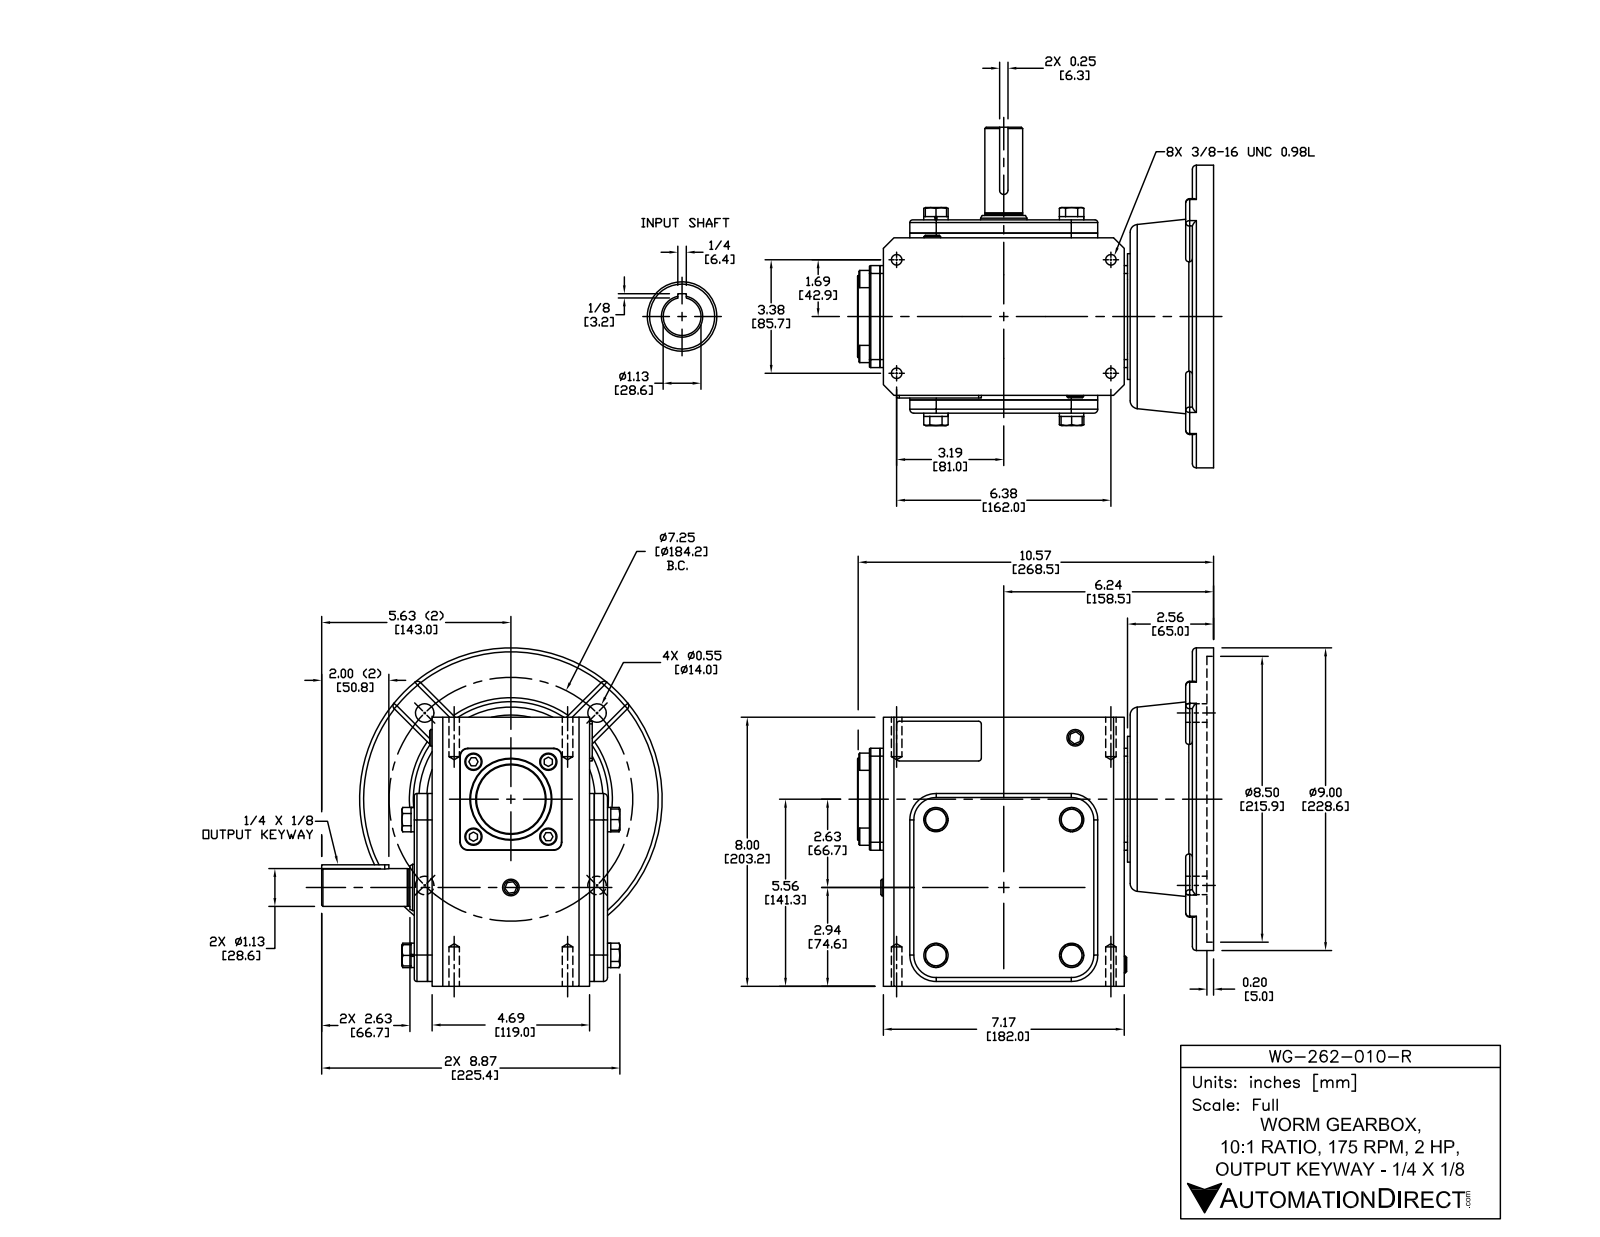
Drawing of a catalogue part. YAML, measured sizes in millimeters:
part_name: "WG-262-010-R"
step_written_by: "SolidWorks 2015 (CONFIG_CONTROL_DESIGN)"
units: millimeters
bodies: {solids: 31, faces: 552, planar: 299, cylindrical: 136, other: 117}
overall_size: [269, 257.3, 255.6]
volume: 5398000
surface_area: 484500
round_holes:
  - {diameter: 8, count: 4}
  - {diameter: 14, count: 4}
  - {diameter: 15, count: 1}
  - {diameter: 28.6, count: 1}
  - {diameter: 35, count: 1}
  - {diameter: 50, count: 1}
  - {diameter: 52, count: 1}
  - {diameter: 97, count: 1}
  - {diameter: 215.9, count: 1}
round_bosses_or_shafts:
  - {diameter: 18.4, count: 4}
  - {diameter: 13, count: 4}
  - {diameter: 228.6, count: 1}
  - {diameter: 62, count: 1}
  - {diameter: 45, count: 1}
  - {diameter: 29, count: 1}
  - {diameter: 28.6, count: 1}
  - {diameter: 28.3, count: 1}
partial_cylinders:
  - {radius: 3, count: 15}
  - {radius: 2, count: 11}
  - {radius: 6, count: 4}
  - {radius: 20, count: 4}
  - {radius: 0.5, count: 2}
  - {radius: 1, count: 2}
  - {radius: 3.2, count: 1}
face_to_face_distances: [126, 10, 136, 13.5, 132.5, 3.5, 122.5, 203.2, 11, 146]
hole_center_spacings: [92.1, 130.2, 65.1, 85.7, 147, 161.9, 183.2, 184.2]
